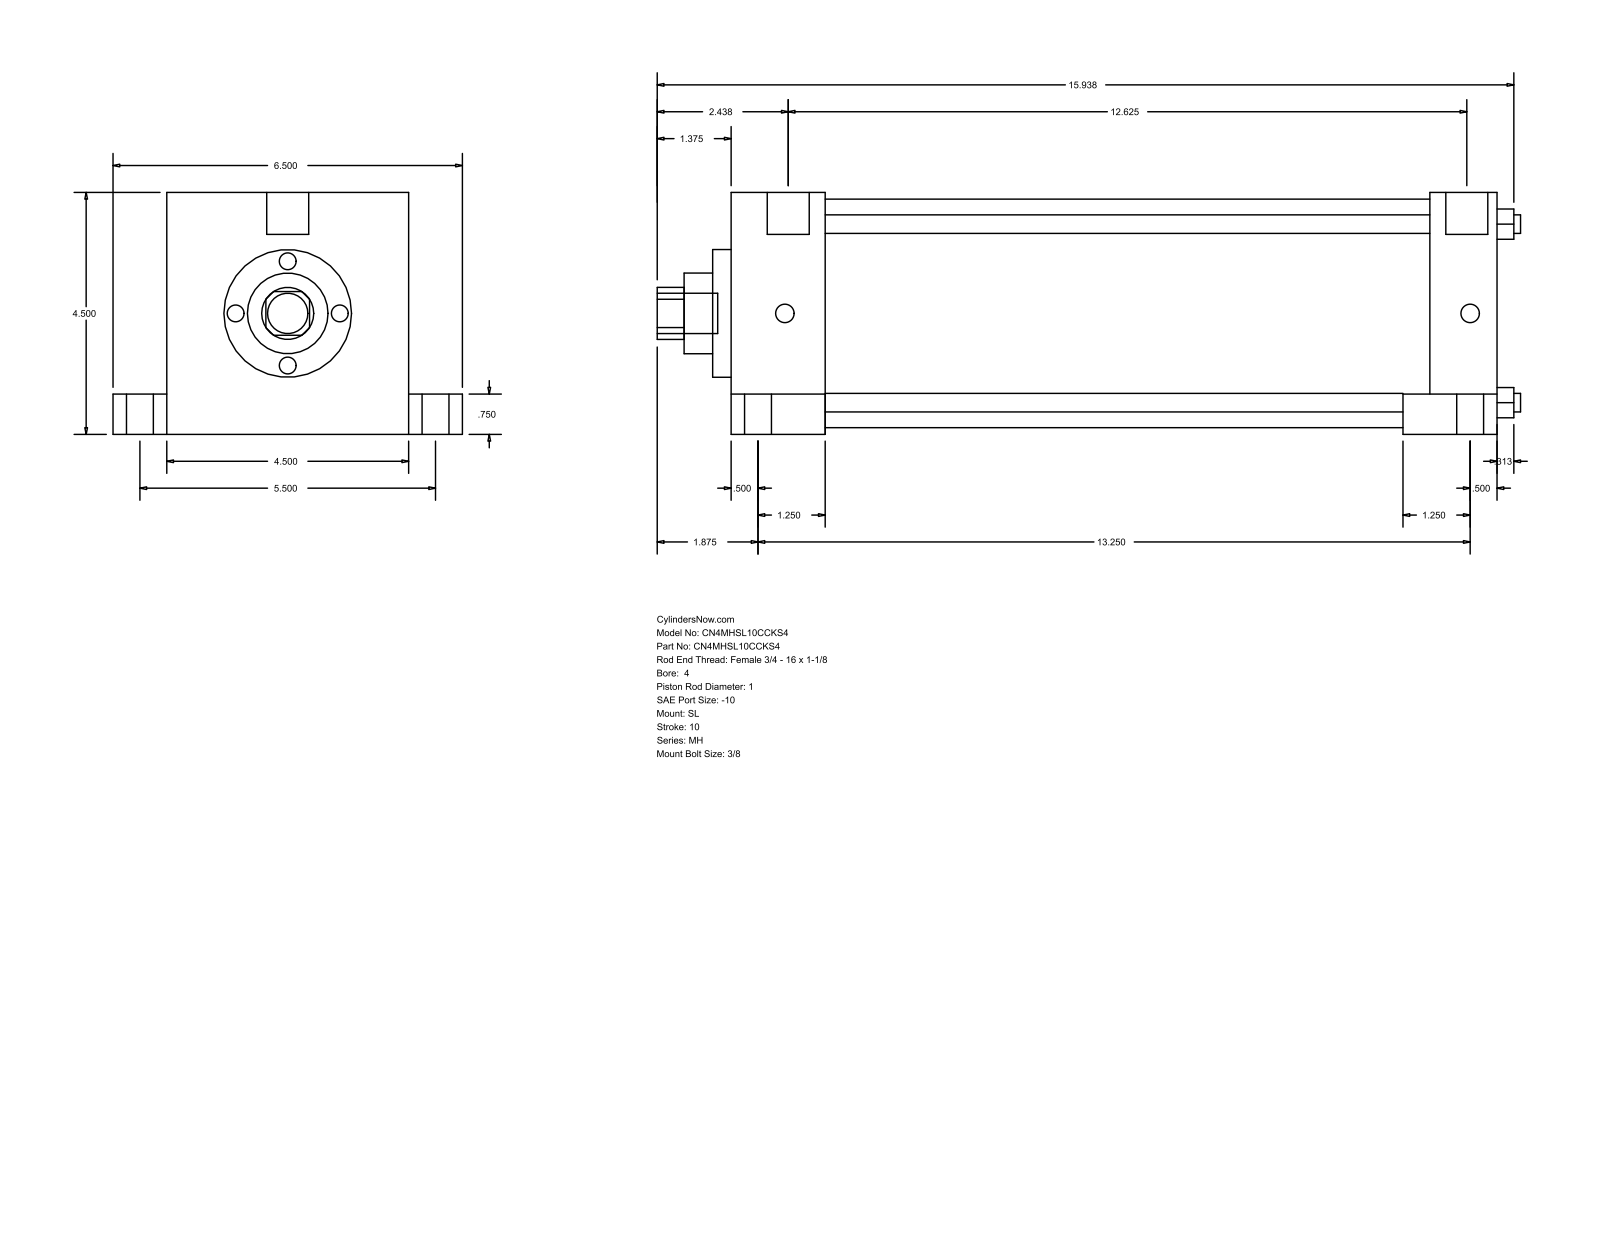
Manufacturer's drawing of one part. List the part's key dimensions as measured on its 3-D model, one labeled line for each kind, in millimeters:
Part name (STEP PRODUCT): MH_SL__0400_1
STEP written by: GSSL Pune (CONFIG_CONTROL_DESIGN)
Units: millimetres
Bodies: 0 solids, 110 faces (77 planar, 33 cylindrical, 0 other)
Overall size (bounding box): 407.99 × 165.1 × 114.3
Round holes (diameter × count): ⌀8.76 ×4, ⌀25.4 ×1, ⌀38.1 ×1, ⌀60.33 ×1, ⌀107.95 ×1
Round bosses / shafts (diameter × count): ⌀19.05 ×5, ⌀12.7 ×4, ⌀8.73 ×4, ⌀19.84 ×2
Partial cylindrical surfaces — rounded edges, fillets, slot ends (radius × count): R12.29 ×1
Main face-to-face distances: 114.3, 361.96, 44.46, 317.5, 330.2, 285.74, 31.76, 25.4, 139.7, 19.05
Hole centre spacings: 59.62, 84.32, 119.25
